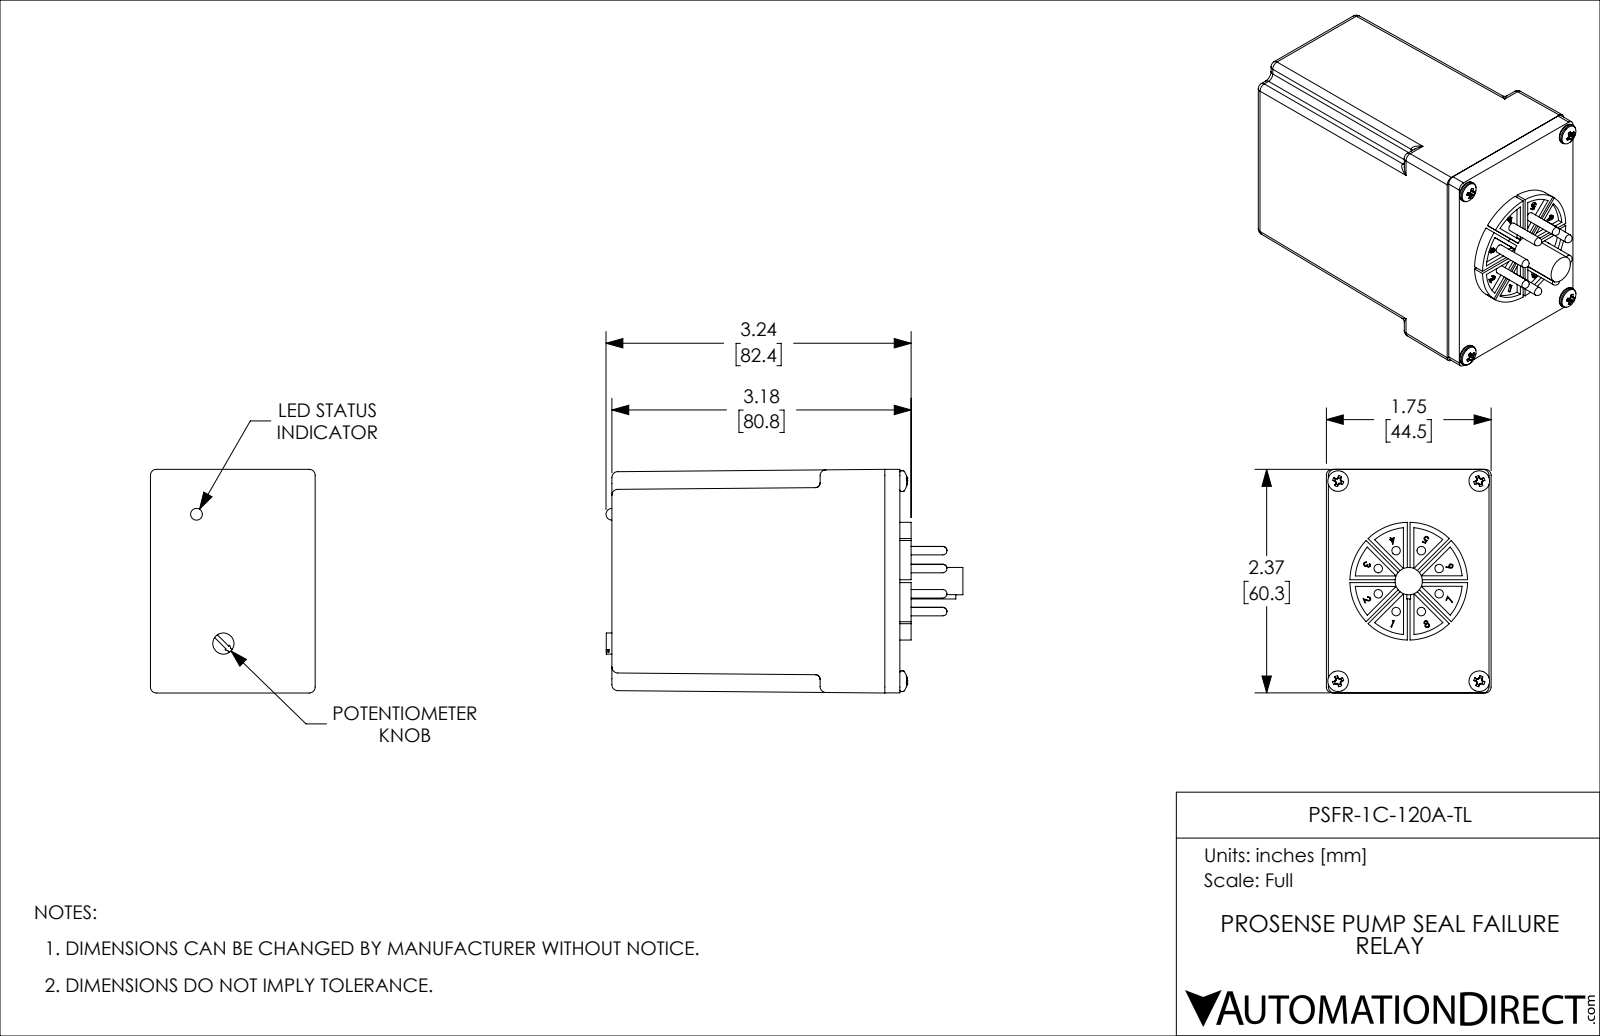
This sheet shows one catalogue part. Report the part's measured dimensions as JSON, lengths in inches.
{"part_name": "PSFR-1C-120A-TL", "step_written_by": "SolidWorks 2019 (CONFIG_CONTROL_DESIGN)", "units": "inches", "bodies": {"solids": 16, "faces": 695, "planar": 229, "cylindrical": 282, "other": 184}, "overall_size": [3.792, 2.375, 1.75], "volume_in3": 12.24, "surface_area_in2": 44.72, "round_holes": [[0.125, 4]], "round_bosses_or_shafts": [[0.09, 8], [0.219, 4], [0.112, 4], [0.08, 4], [1.25, 1], [0.29, 1], [0.225, 1]], "partial_cylinders_radius": [[0.063, 32], [0.005, 8], [0.05, 4], [0.57, 1]], "face_to_face_distances": [2.9, 0.16, 3.06, 0.07, 0.23, 3.13, 0.188, 0.03, 3.18, 0.05], "hole_center_spacings": [1.5, 2.125, 2.601]}
